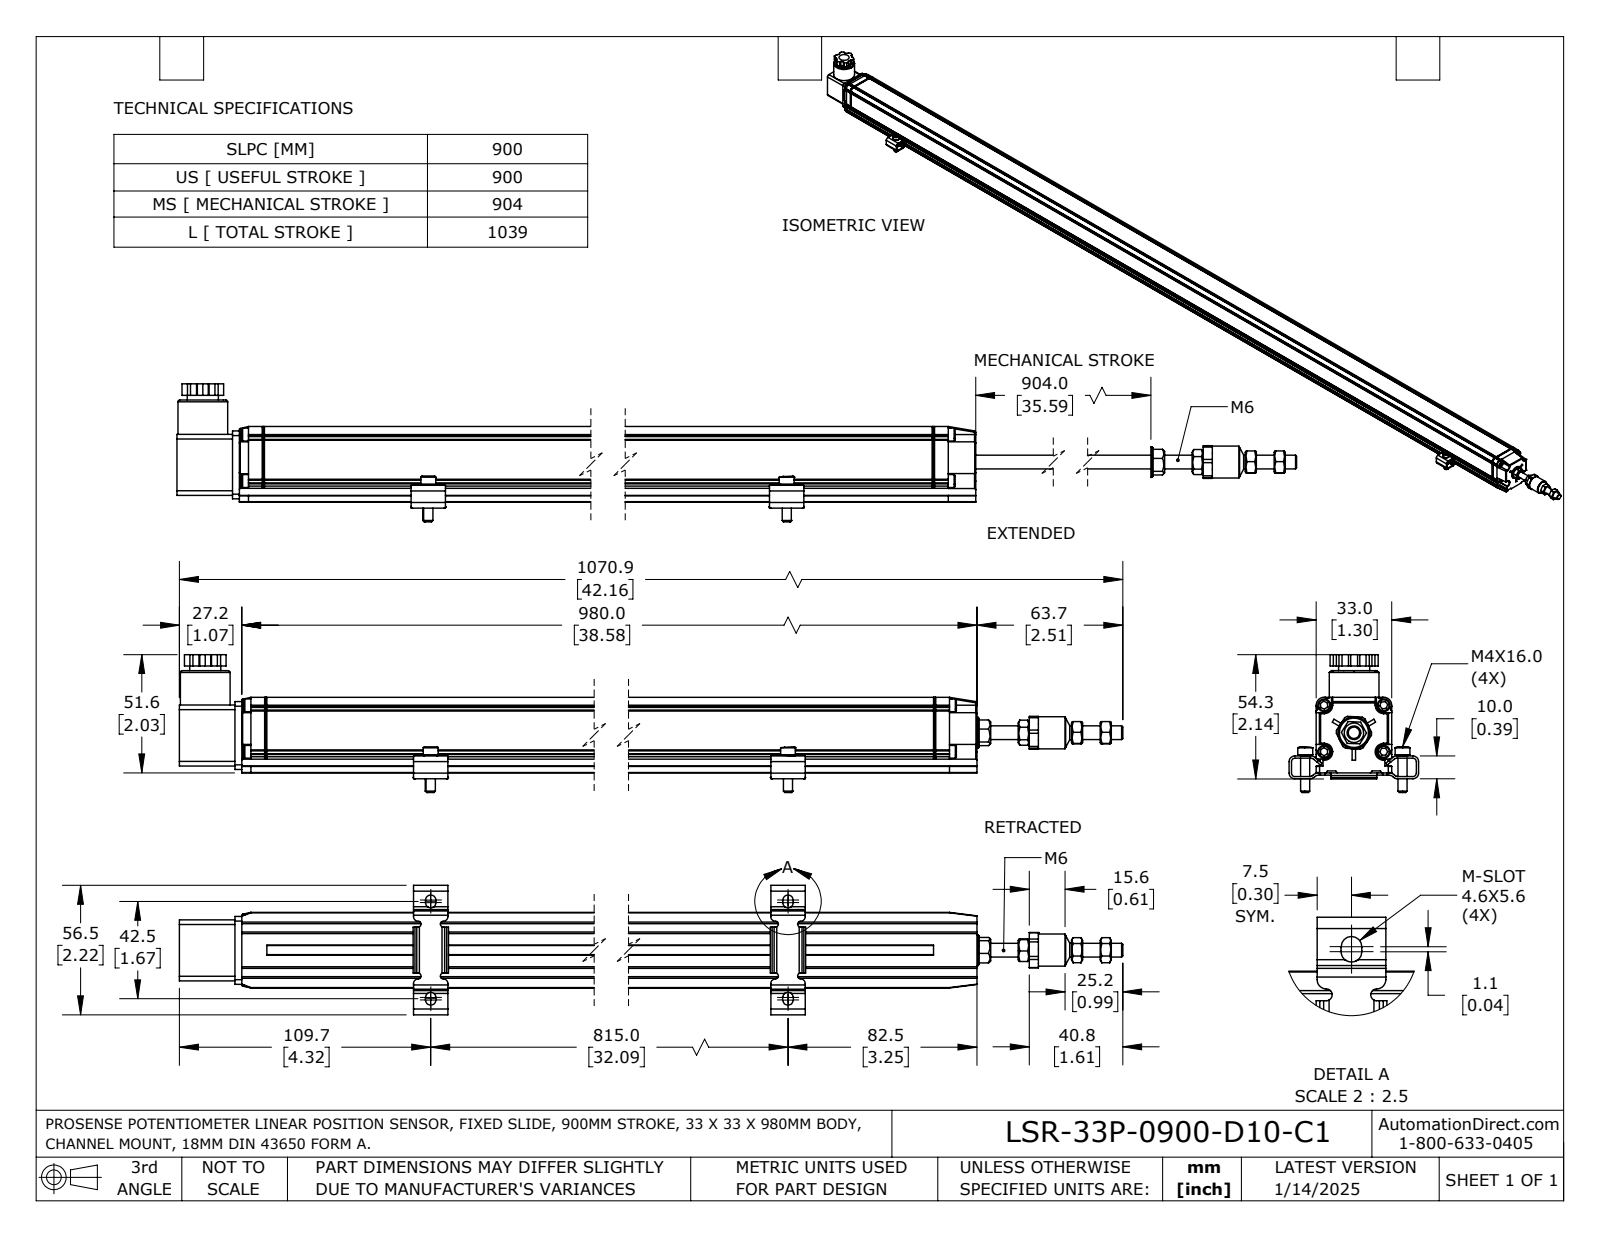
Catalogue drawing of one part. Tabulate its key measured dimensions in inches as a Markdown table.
| quantity | value |
| --- | --- |
| part name | LSR-33P-0900-D10-C1 |
| STEP written by | SolidWorks 2023 (AUTOMOTIVE_DESIGN) |
| units | inches |
| bodies | 14 solids, 995 faces (641 planar, 269 cylindrical, 85 other) |
| overall size | 42.159 × 2.37 × 2.224 |
| volume | 59.71 in³ |
| surface area | 352.4 in² |
| round holes (diameter × count) | 0.106 × 4, 0.13 × 4, 0.169 × 1, 0.205 × 1, 0.209 × 1, 0.232 × 1, 0.276 × 1, 0.285 × 1, 0.394 × 1, 0.413 × 1, 0.573 × 1, 0.602 × 1 |
| round bosses / shafts (diameter × count) | 0.157 × 5, 0.118 × 5, 0.256 × 4, 0.22 × 4, 0.854 × 1, 0.551 × 1, 0.535 × 1, 0.528 × 1 |
| partial cylindrical surfaces (radius × count) | 0.079 × 28, 0.02 × 23, 0.008 × 16, 0.051 × 8, 0.059 × 8, 0.089 × 8, 0.118 × 8, 0.039 × 4 |
| main face-to-face distances | 1.299, 0.118, 0.22, 1.181, 1.079, 0.079, 0.039, 0.142, 1.22, 0.185 |
| hole center spacings | 0.047, 0.583, 0.607, 0.696, 0.73, 0.799, 1.024, 1.299 |
